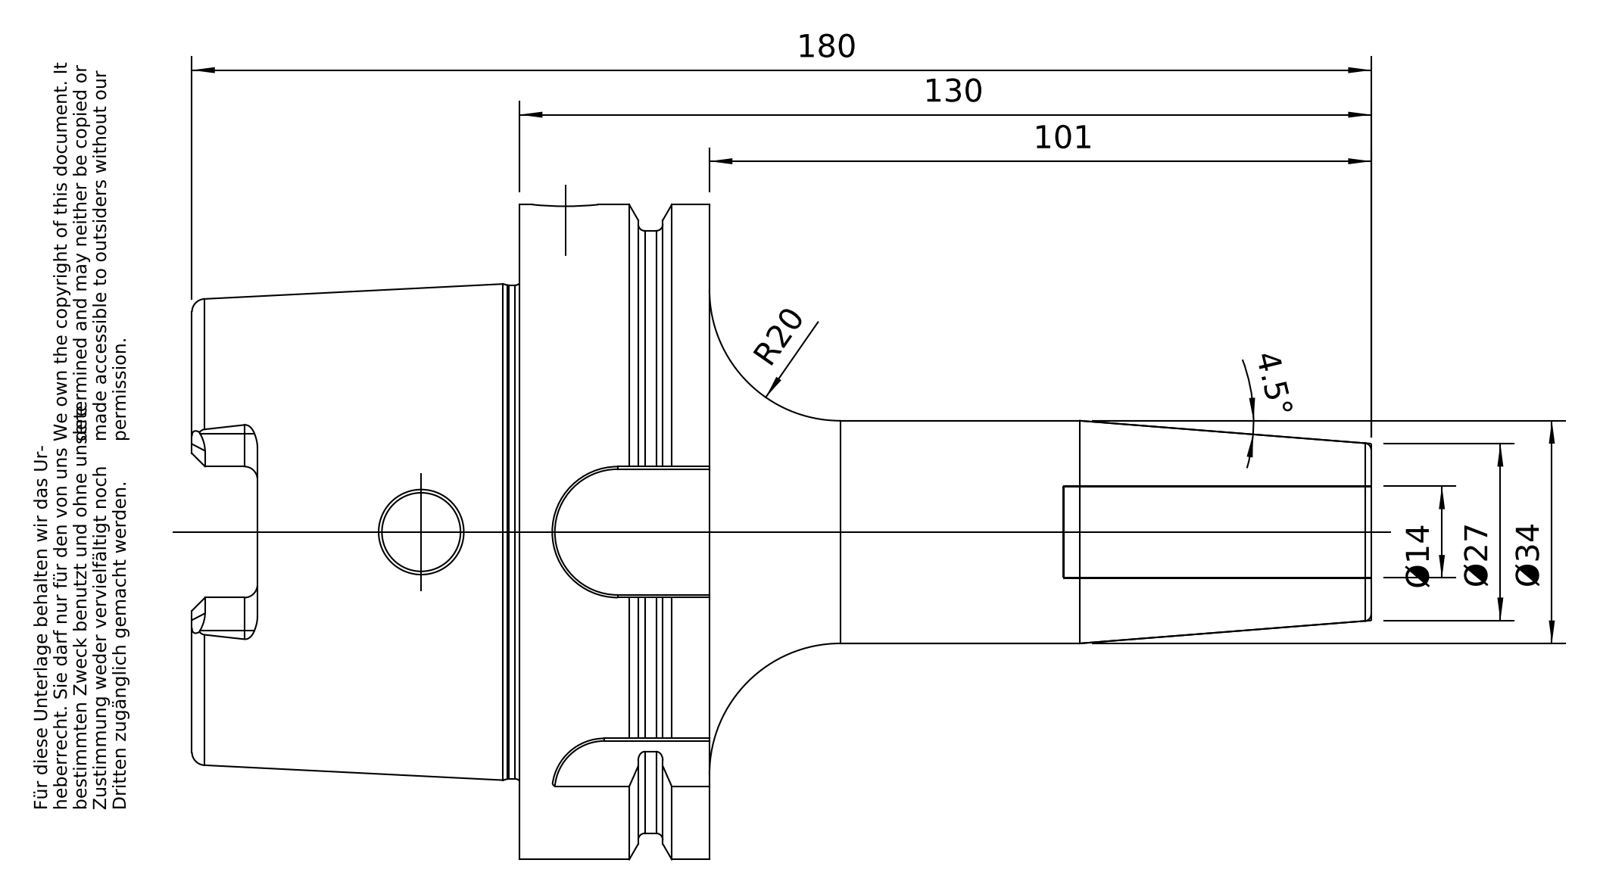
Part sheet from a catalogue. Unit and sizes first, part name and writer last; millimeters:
Units: millimetres
Overall size (bounding box): 180 × 100 × 100
Round holes (diameter × count): ⌀10 ×1, ⌀12 ×1, ⌀14 ×1, ⌀22.5 ×1, ⌀24 ×1, ⌀24.32 ×1, ⌀24.5 ×1, ⌀53 ×1, ⌀63 ×1
Round bosses / shafts (diameter × count): ⌀100 ×1, ⌀92 ×1, ⌀75.36 ×1, ⌀34 ×1
Partial cylindrical surfaces — rounded edges, fillets, slot ends (radius × count): R2 ×6, R5 ×4, R8 ×1, R10 ×1, R11 ×1
Main face-to-face distances: 29, 12.5, 16.5, 50, 62.5, 79, 88, 78.5, 28.5, 16
Volume: 342 496 mm³ · Surface area: 61 511 mm²
Bodies: 1 solid, 174 faces (50 planar, 51 cylindrical, 73 other)
Part name (STEP PRODUCT): A100-144-14
STEP written by: PRO/ENGINEER BY PARAMETRIC TECHNOLOGY CORPORATION, 2010430 (CONFIG_CONTROL_DESIGN)
